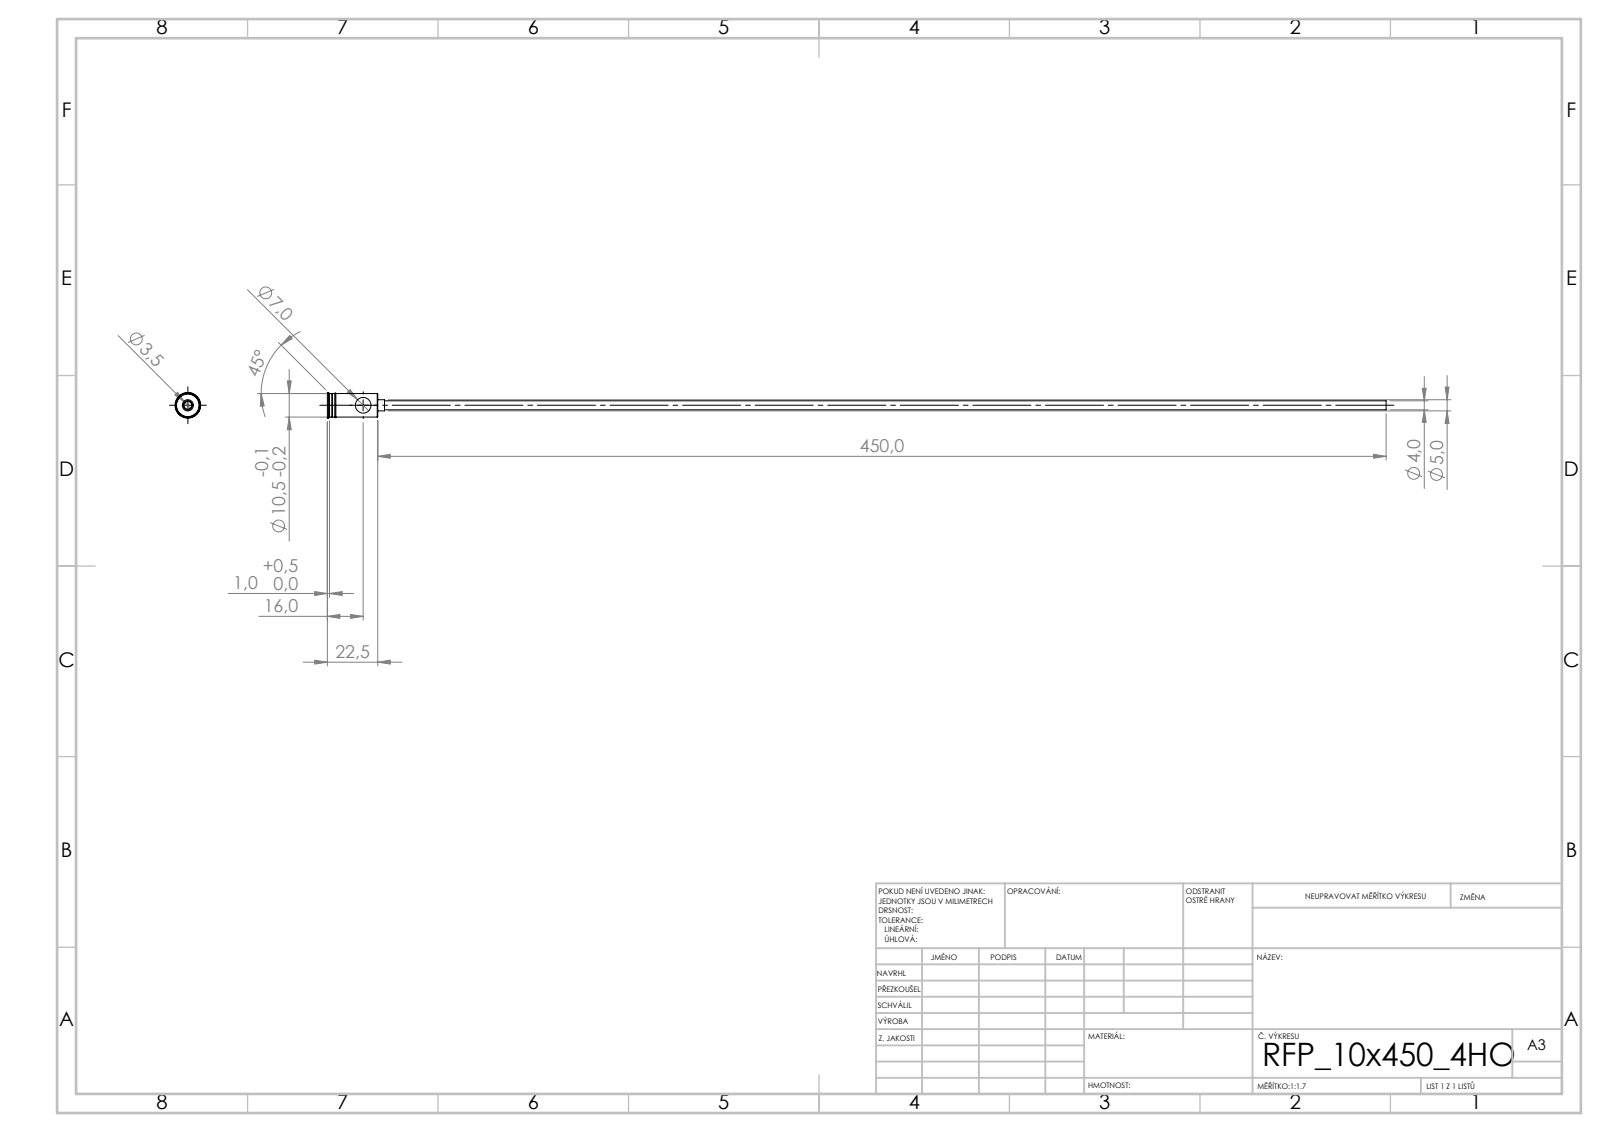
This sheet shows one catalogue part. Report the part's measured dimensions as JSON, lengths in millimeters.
{"step_written_by": "SolidWorks 2019 (CONFIG_CONTROL_DESIGN)", "units": "millimeters", "bodies": {"solids": 1, "faces": 44, "planar": 20, "cylindrical": 16, "other": 8}, "overall_size": [472.5, 11.5, 11.5], "volume_mm3": 2839, "surface_area_mm2": 11752, "round_holes": [[3.5, 1], [7, 1]], "round_bosses_or_shafts": [[11.5, 1], [10.5, 1], [5, 1], [4, 1]], "face_to_face_distances": [22.5, 20.5, 2, 5.9, 20.2, 2.3, 3, 23.2, 23.5, 25.5]}
